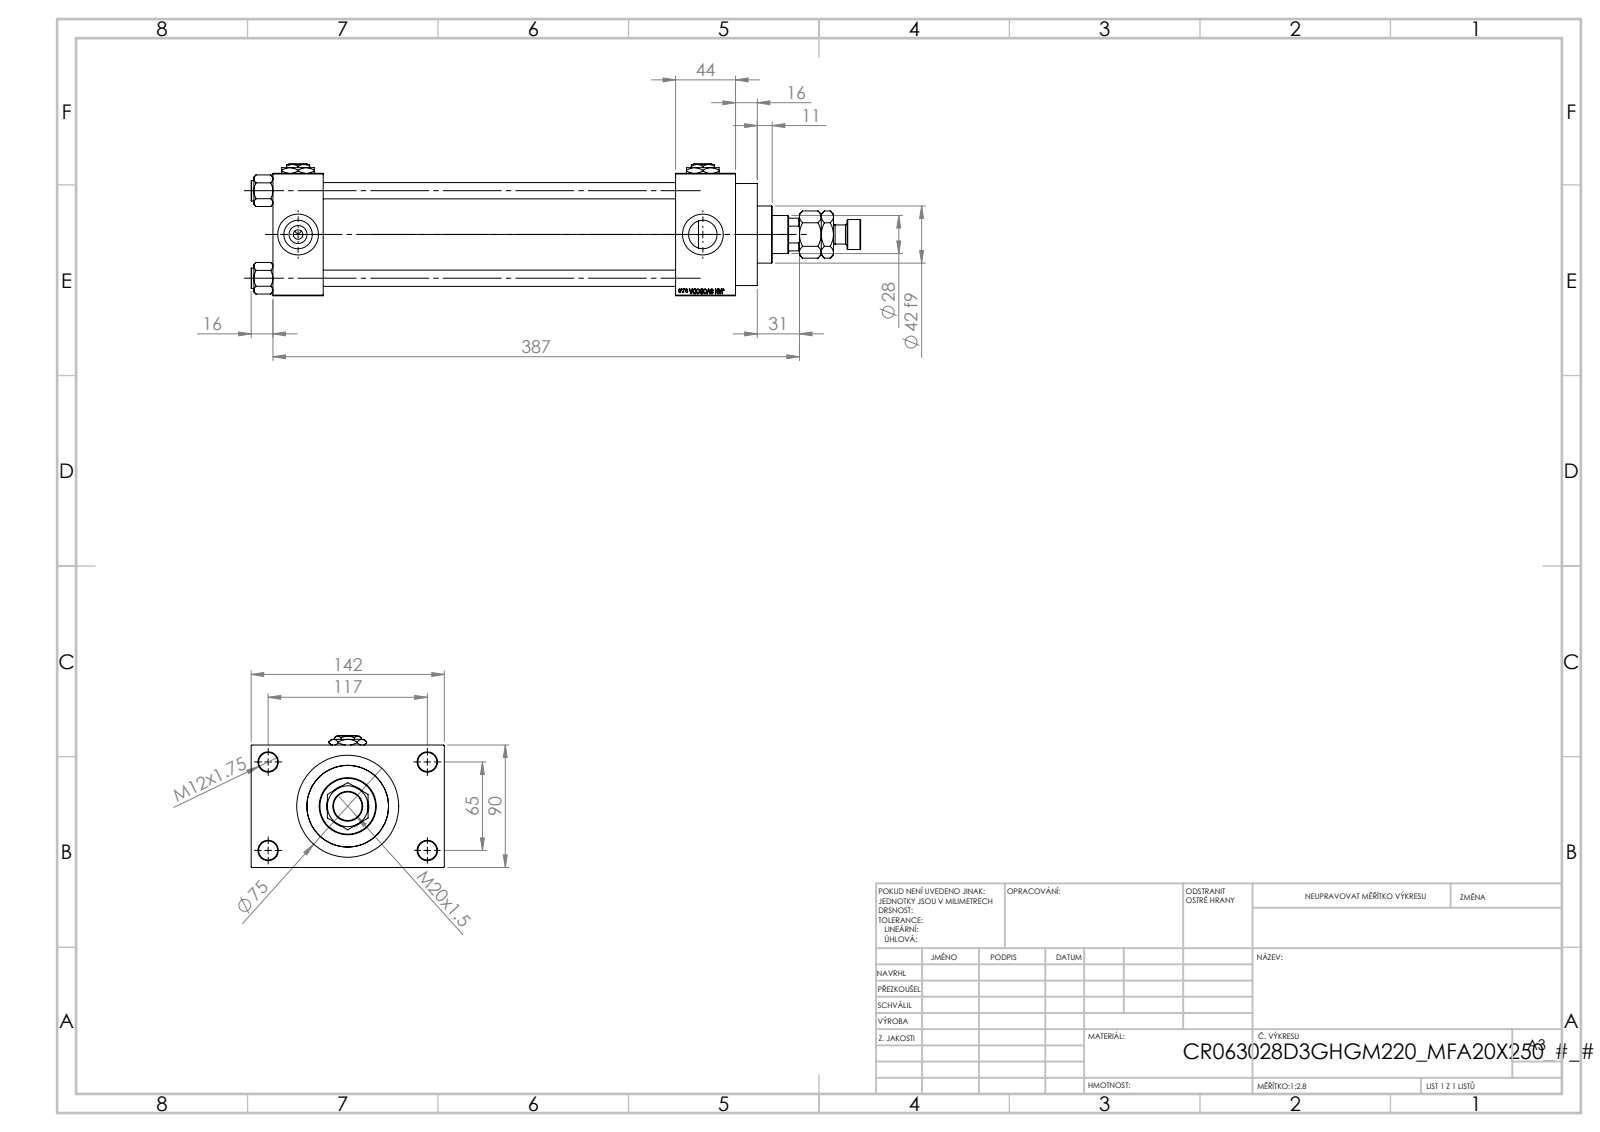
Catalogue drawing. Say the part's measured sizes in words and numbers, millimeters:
The part is named "NUT_M5_D; V215CR_D_TYCINKA; V215CR_VCP_D; MFA (+3 more)". Its 3-D file was written by "SolidWorks 2019 (CONFIG_CONTROL_DESIGN)". It is 14 solids with 1256 faces: 561 planar, 103 cylindrical and 592 other. Overall it measures 448 by 142 by 97 millimeters. Its volume is 1 453 000 cubic millimeters and its surface area 341 222 square millimeters. Round holes: 4 of diameter 12, 4 of diameter 14, 4 of diameter 20.96, 4 of diameter 30, 3 of diameter 7, 1 of diameter 18.5, 1 of diameter 28, 1 of diameter 31, 1 of diameter 50, 1 of diameter 60, 1 of diameter 63. Round bosses or shafts: 4 of diameter 15, 1 of diameter 75, 1 of diameter 69, 1 of diameter 42, 1 of diameter 22, 1 of diameter 14. Partial cylindrical surfaces (rounded edges, fillets, slot ends): 1 of radius 13.5. The main face-to-face distances are 90, 259, 37, 296, 303, 340, 44, 116, 26, 356. The hole center spacings are 26.35, 45.47, 64.3, 66.92, 69.81, 90.65, 111.34, 65.
